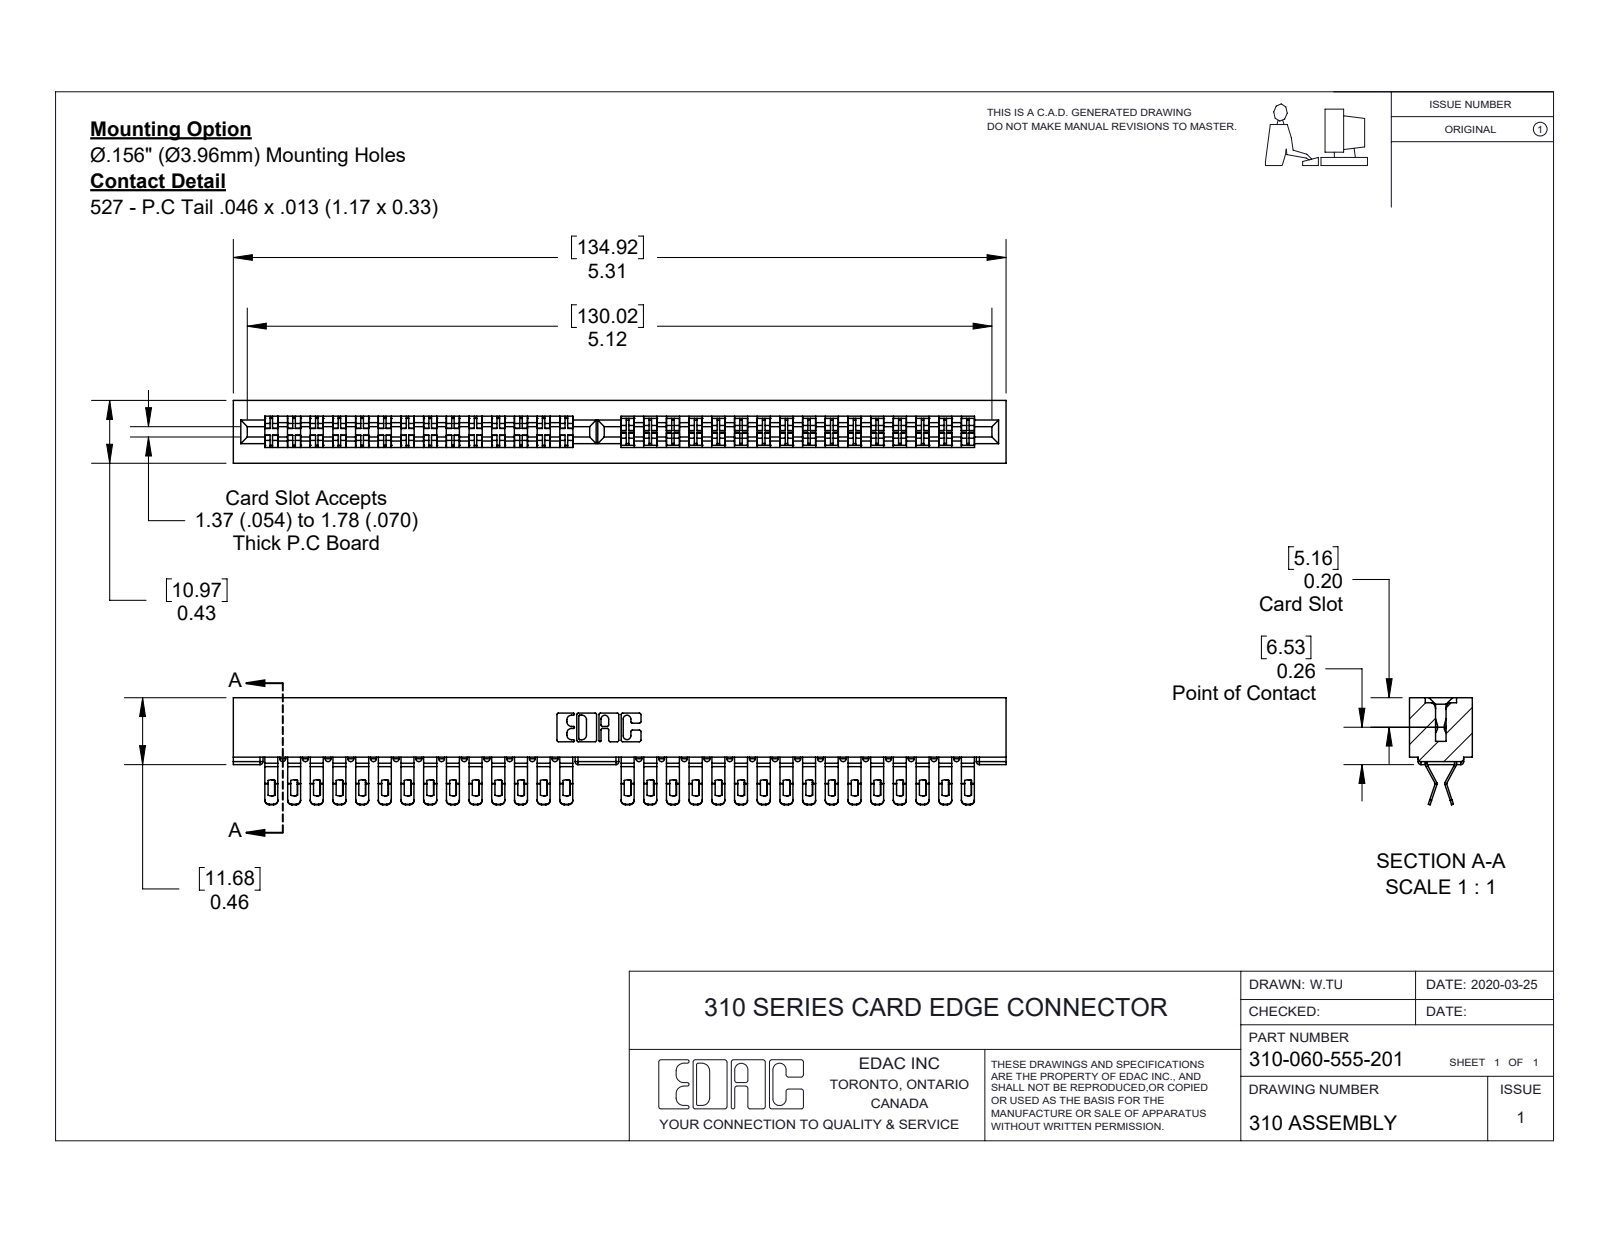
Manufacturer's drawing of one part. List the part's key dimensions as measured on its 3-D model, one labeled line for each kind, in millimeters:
Part name (STEP PRODUCT): 307-290-001_555; 310-060-555-201; 310 Part_No Mounting Lugs
STEP written by: SolidWorks 2016 (CONFIG_CONTROL_DESIGN)
Units: millimetres
Bodies: 61 solids, 3818 faces (2120 planar, 1634 cylindrical, 64 other)
Overall size (bounding box): 134.93 × 18.69 × 10.97
Volume: 12 189 mm³ · Surface area: 18 018 mm²
Partial cylindrical surfaces — rounded edges, fillets, slot ends (radius × count): R0.76 ×120, R1.57 ×120, R0.51 ×98, R0.25 ×22, R0.17 ×6, R0.8 ×6, R0.3 ×4, R0.38 ×4
Main face-to-face distances: 0.33, 2.76, 8.22, 0.38, 10.98, 4.75, 5.46, 1.82, 3.14, 7.84
